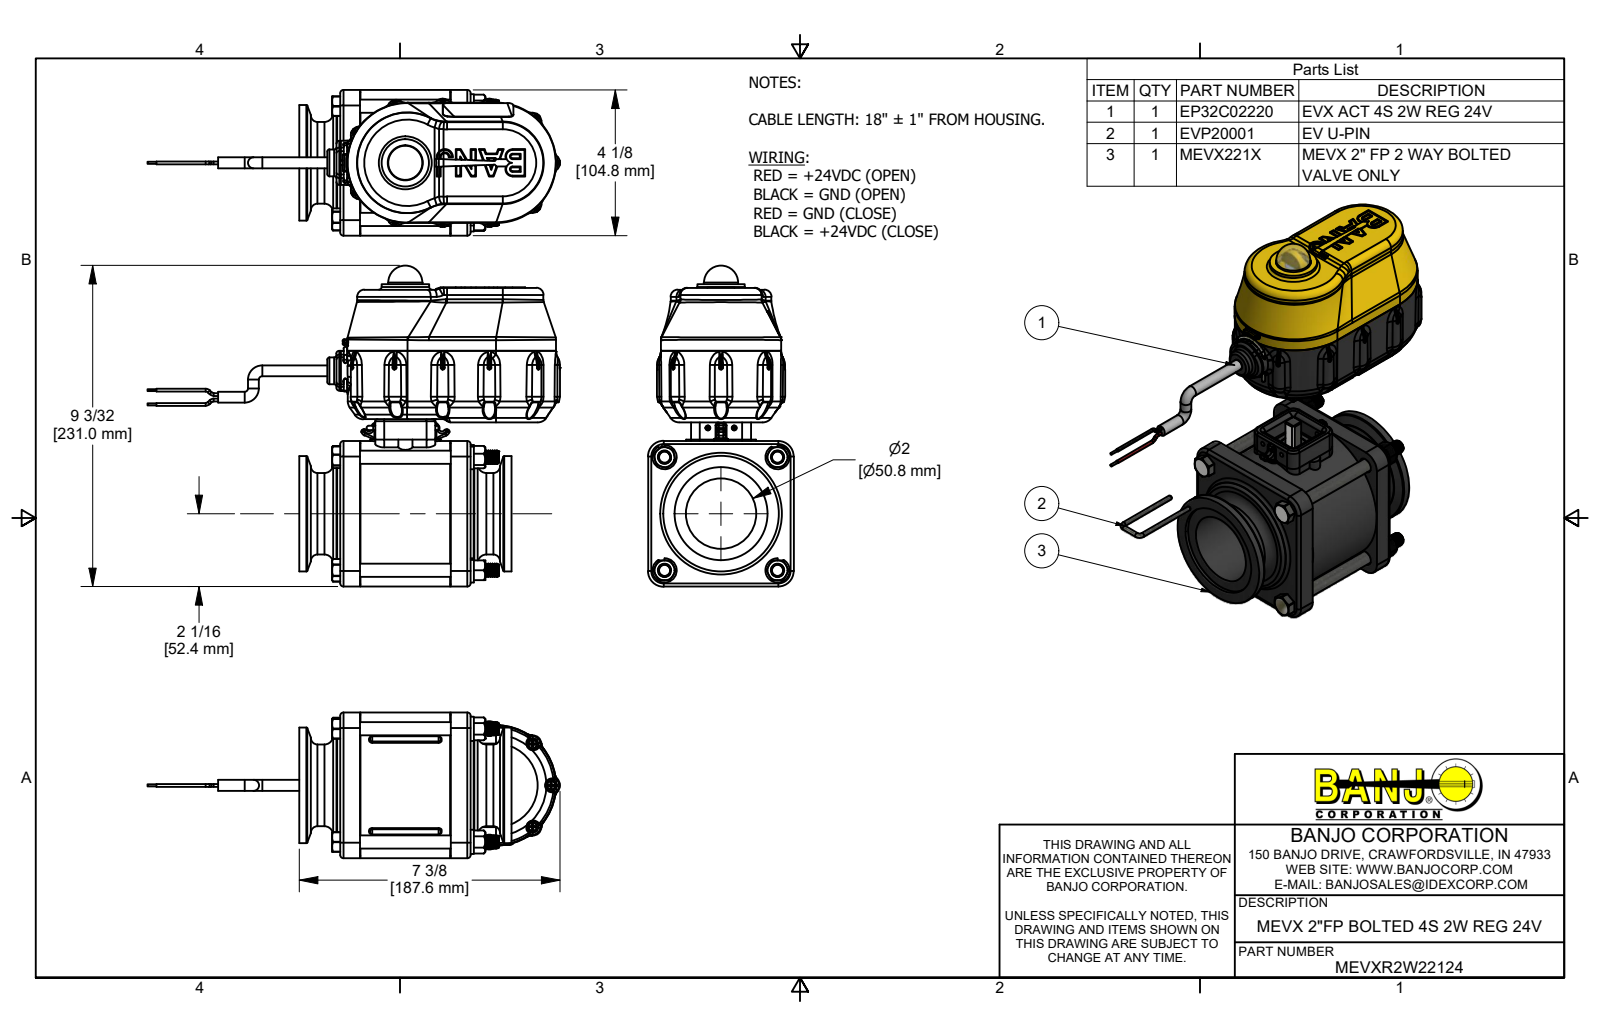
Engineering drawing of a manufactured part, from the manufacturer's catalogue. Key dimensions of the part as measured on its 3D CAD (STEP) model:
Part name (STEP PRODUCT): MEVXR2W22124; EP32C02220; 91400A119; 95584A200 (+8 more)
STEP written by: Autodesk Inventor 2019 (AUTOMOTIVE_DESIGN)
Units: inches
Bodies: 95 solids, 12297 faces (3490 planar, 3287 cylindrical, 5520 other)
Overall size (bounding box): 11.685 × 9.095 × 4.125
Volume: 71.22 in³ · Surface area: 741.6 in²
Round holes (diameter × count): ⌀0.15 ×13, ⌀0.095 ×11, ⌀0.107 ×4, ⌀0.126 ×4, ⌀0.136 ×4, ⌀0.17 ×4, ⌀0.307 ×4, ⌀0.385 ×4, ⌀0.438 ×4, ⌀0.089 ×2, ⌀0.105 ×2, ⌀0.115 ×2
Round bosses / shafts (diameter × count): ⌀0.324 ×60, ⌀0.25 ×17, ⌀0.14 ×11, ⌀0.108 ×11, ⌀0.085 ×11, ⌀0.08 ×10, ⌀0.375 ×5, ⌀0.687 ×4
Partial cylindrical surfaces — rounded edges, fillets, slot ends (radius × count): R0.04 ×147, R0.02 ×87, R0.01 ×56, R0.005 ×43, R0.03 ×34, R0.06 ×28, R0.08 ×28, R0.1 ×22
Main face-to-face distances: 0.1, 2.565, 2.41, 0.56, 3.13, 1.78, 0.72, 2.97, 0.16, 1.685
Hole centre spacings: 1.283, 2.265, 3.204, 2.73, 2.967, 3.45, 4.214, 0.487
